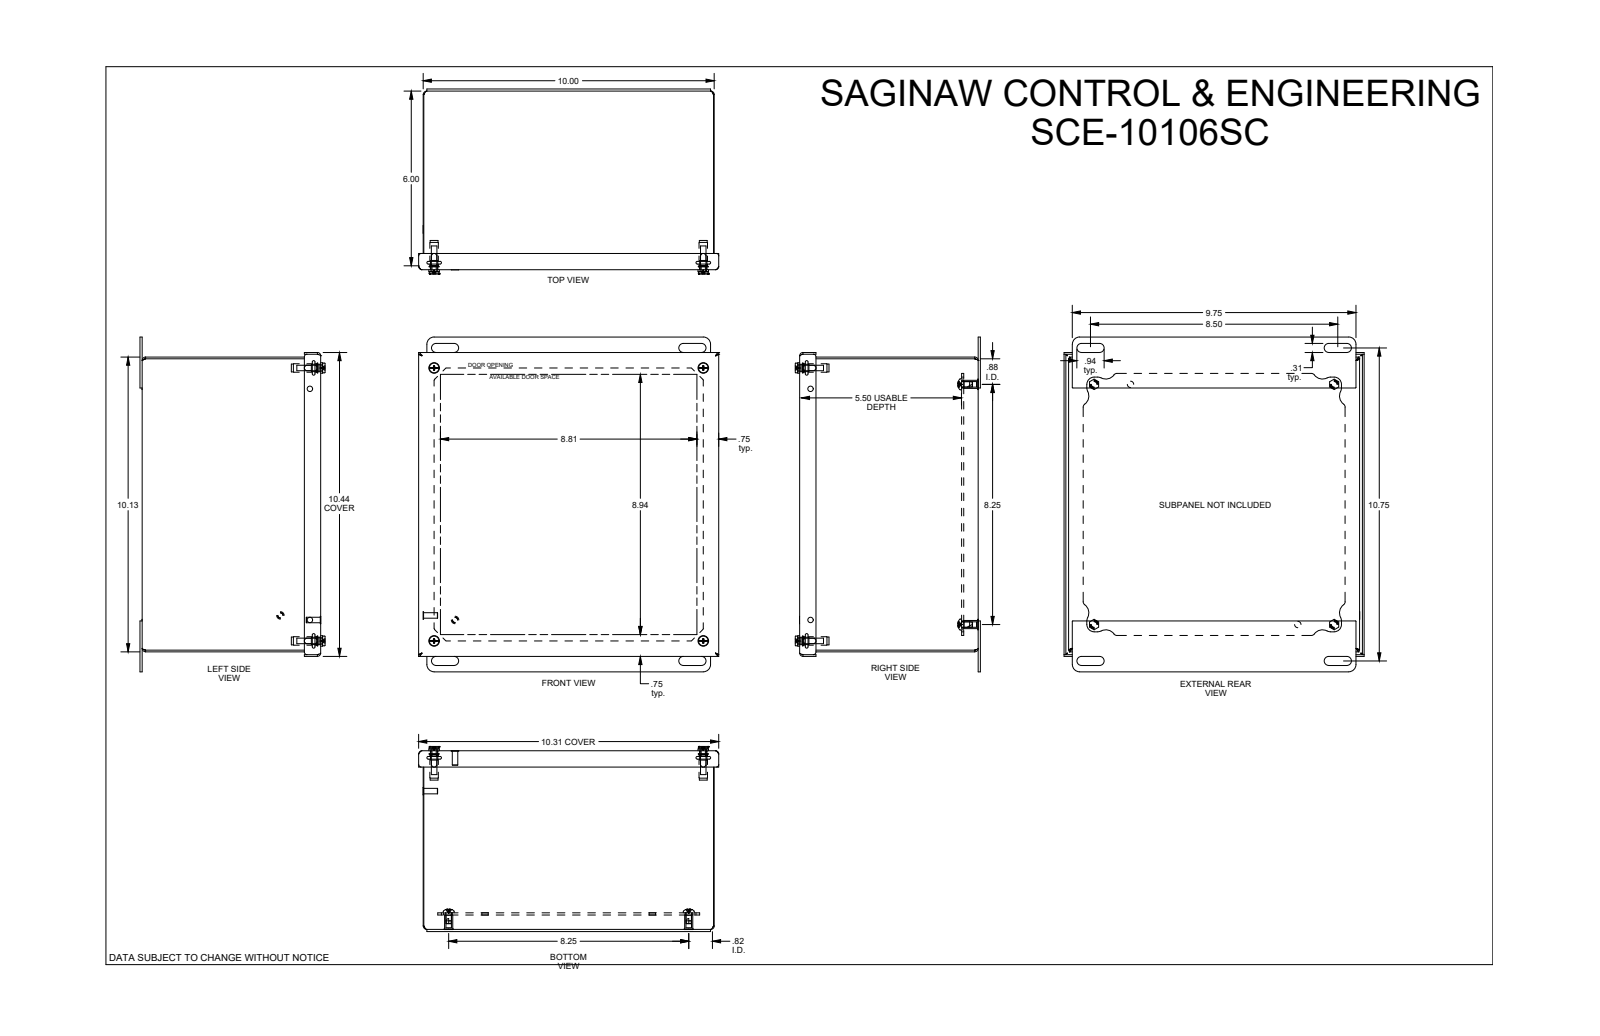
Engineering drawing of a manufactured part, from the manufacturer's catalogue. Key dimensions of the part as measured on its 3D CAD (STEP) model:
Part name (STEP PRODUCT): SCE-10106SC
STEP written by: SolidWorks 2019 (AUTOMOTIVE_DESIGN)
Units: inches
Bodies: 28 solids, 805 faces (328 planar, 207 cylindrical, 270 other)
Overall size (bounding box): 11.5 × 10.313 × 6.361
Volume: 38.45 in³ · Surface area: 1 234 in²
Round holes (diameter × count): ⌀0.19 ×8, ⌀0.25 ×8, ⌀0.22 ×4, ⌀0.266 ×4, ⌀0.281 ×4, ⌀0.317 ×4, ⌀0.187 ×2, ⌀0.218 ×2, ⌀0.193 ×1
Round bosses / shafts (diameter × count): ⌀0.188 ×10, ⌀0.437 ×4, ⌀0.373 ×4, ⌀0.362 ×4, ⌀0.34 ×4, ⌀0.334 ×4, ⌀0.292 ×4, ⌀0.28 ×4
Partial cylindrical surfaces — rounded edges, fillets, slot ends (radius × count): R0.125 ×16, R0.25 ×16, R0.06 ×12, R0.005 ×8, R0.05 ×8, R0.063 ×8, R0.156 ×8, R0.255 ×8
Main face-to-face distances: 0.06, 6.075, 9.94, 6.135, 6.015, 5.505, 0.075, 0.57, 0.51, 5.565
Hole centre spacings: 0.753, 8.827, 8.25, 8.768, 12.419, 9.375, 12.419, 8.768
